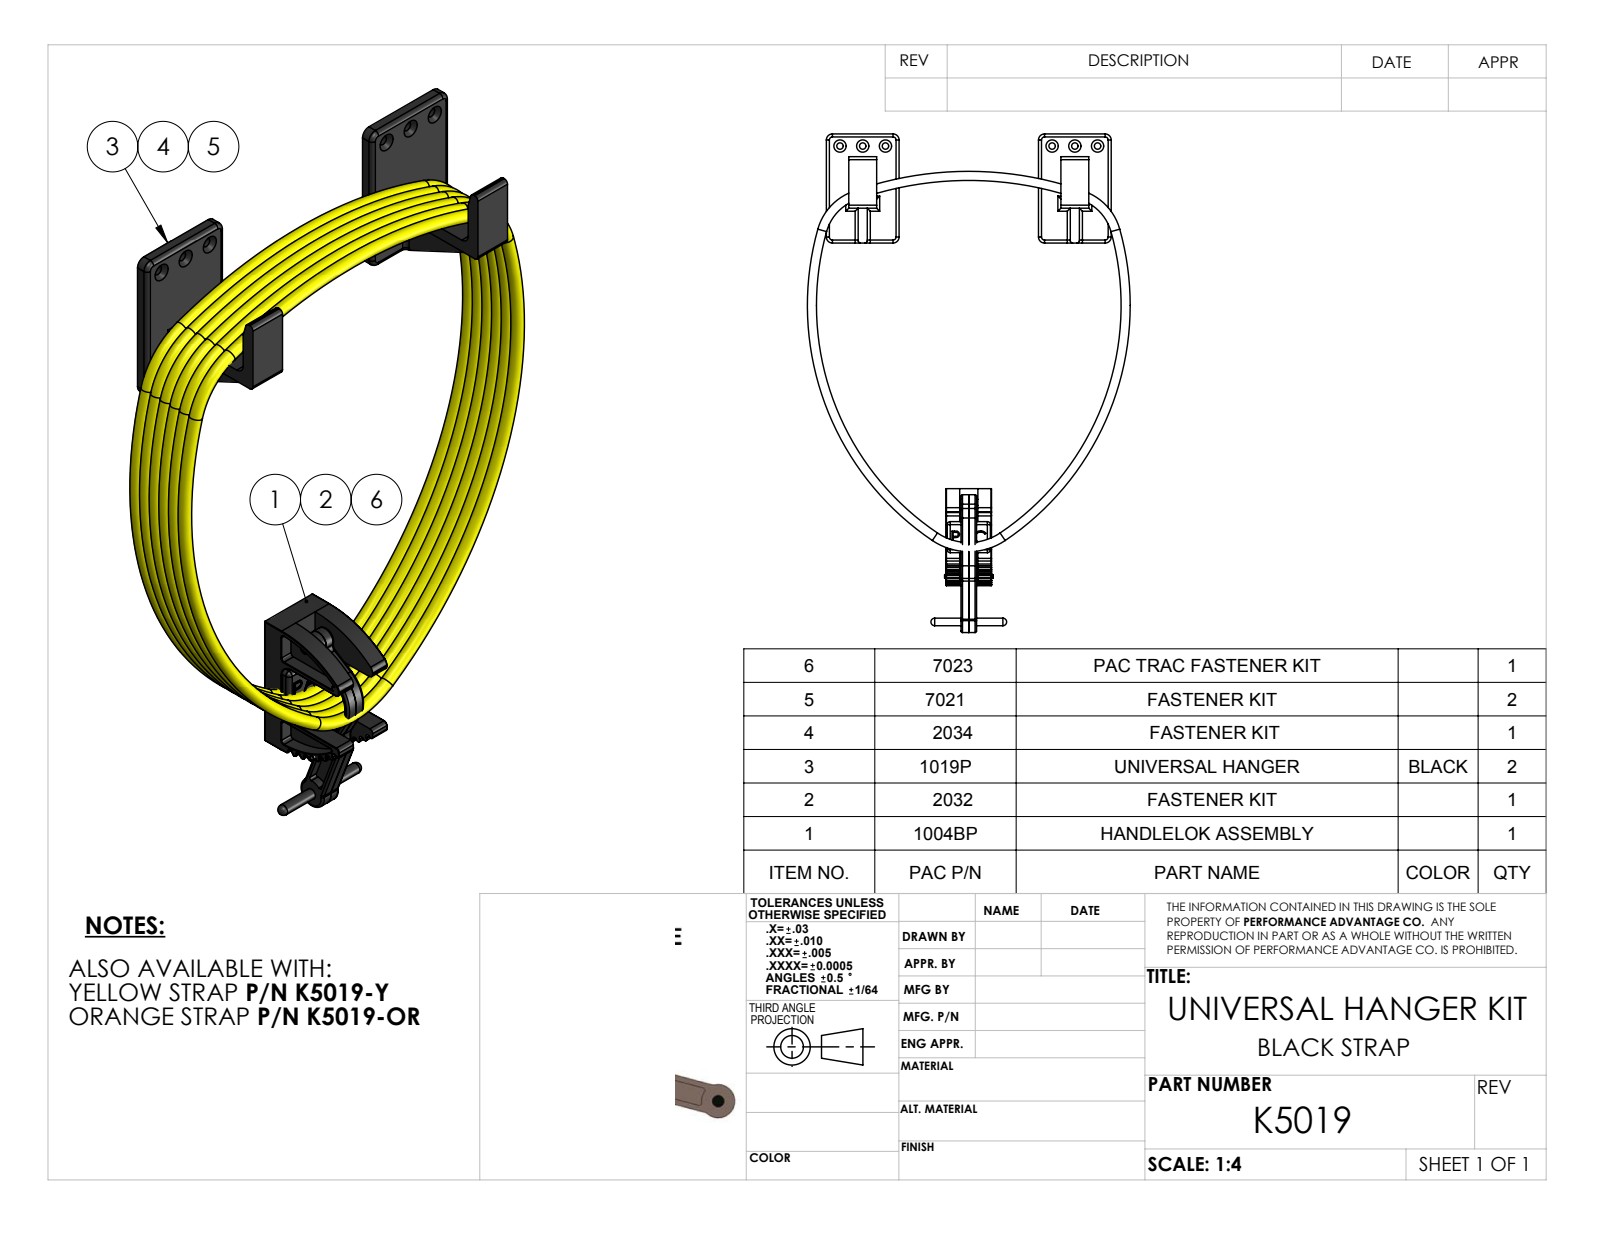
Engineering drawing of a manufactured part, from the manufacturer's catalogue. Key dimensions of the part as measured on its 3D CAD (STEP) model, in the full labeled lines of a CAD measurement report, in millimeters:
Part name (STEP PRODUCT): K5019; 1004_In use; 1004 BASE; 1004 PIVOT PIN (+4 more)
STEP written by: SolidWorks 2010 (CONFIG_CONTROL_DESIGN)
Units: millimetres
Bodies: 15 solids, 1052 faces (306 planar, 406 cylindrical, 340 other)
Overall size (bounding box): 521.5 × 338.2 × 90.6
Volume: 860 300 mm³ · Surface area: 338 500 mm²
Round holes (diameter × count): ⌀6.8 ×8, ⌀13.5 ×6, ⌀4.3 ×4, ⌀4 ×1, ⌀4 ×1, ⌀6.4 ×1, ⌀8 ×1
Round bosses / shafts (diameter × count): ⌀4.7 ×4, ⌀4.1 ×4, ⌀5.2 ×3, ⌀15.9 ×1, ⌀5.2 ×1
Partial cylindrical surfaces — rounded edges, fillets, slot ends (radius × count): R0.4 ×68, R1 ×32, R3.2 ×31, R6.4 ×12, R1.6 ×11, R1.6 ×8, R1.7 ×7, R1.8 ×7
Main face-to-face distances: 9.5, 3.2, 23.8, 14.3, 9.5, 222.3, 9.8, 19.4, 47.6, 16.7
Hole centre spacings: 21, 33.5, 442.1, 14.3, 23.8, 23.8, 25.4, 29.1
